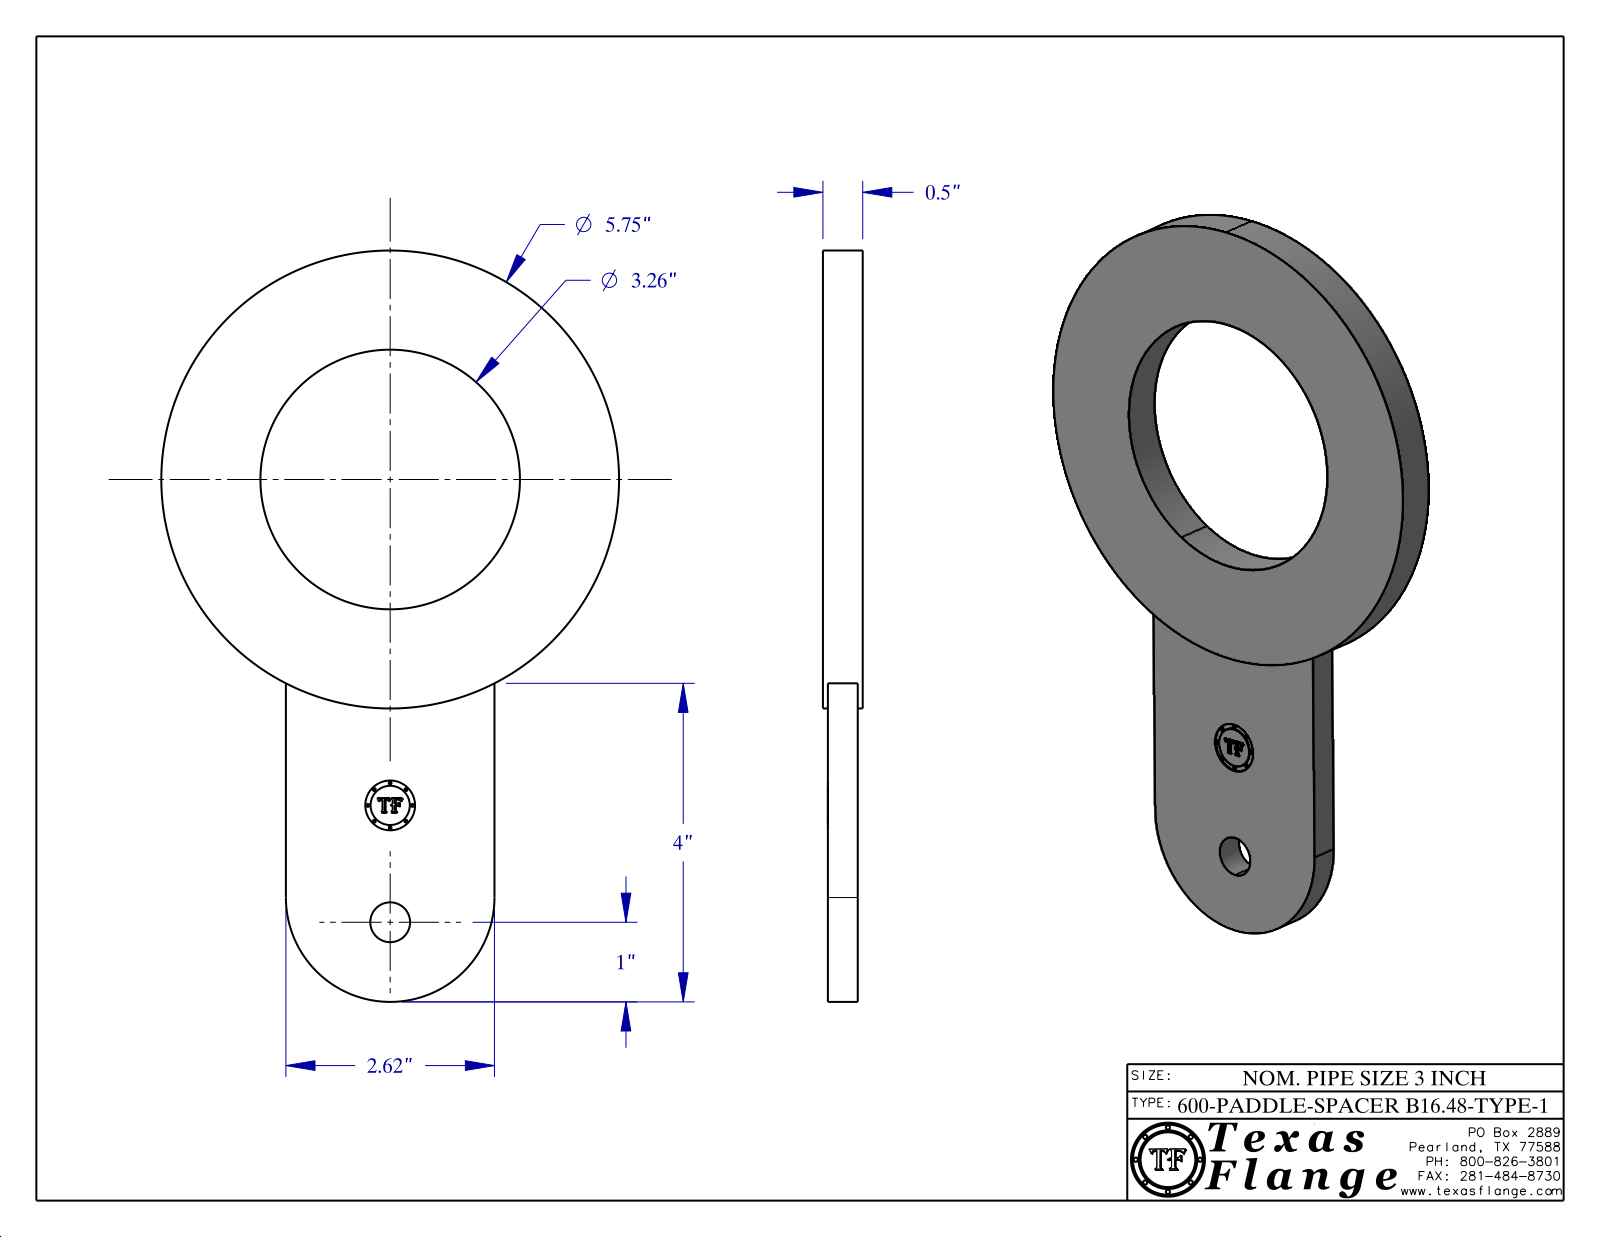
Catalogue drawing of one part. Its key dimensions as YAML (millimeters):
part_name: "3-600-PADDLE-SPACER-B16.48-TYPE-2"
step_written_by: "CATIA V5 STEP AP214 (AUTOMOTIVE_DESIGN)"
units: millimeters
bodies: {solids: 1, faces: 398, planar: 371, cylindrical: 27, other: 0}
overall_size: [239.6, 146.1, 12.7]
volume: 199600
surface_area: 45560
round_holes:
  - {diameter: 12.7, count: 1}
  - {diameter: 15.9, count: 1}
  - {diameter: 82.8, count: 1}
round_bosses_or_shafts:
  - {diameter: 1, count: 8}
  - {diameter: 146.1, count: 1}
  - {diameter: 12.5, count: 1}
partial_cylinders:
  - {radius: 33.3, count: 1}
face_to_face_distances: [1.6, 11.1, 12.7, 9.5, 66.5, 10.7, 9.1, 0.4, 2, 31.7]
hole_center_spacings: [37.3, 103.9, 141.2]
